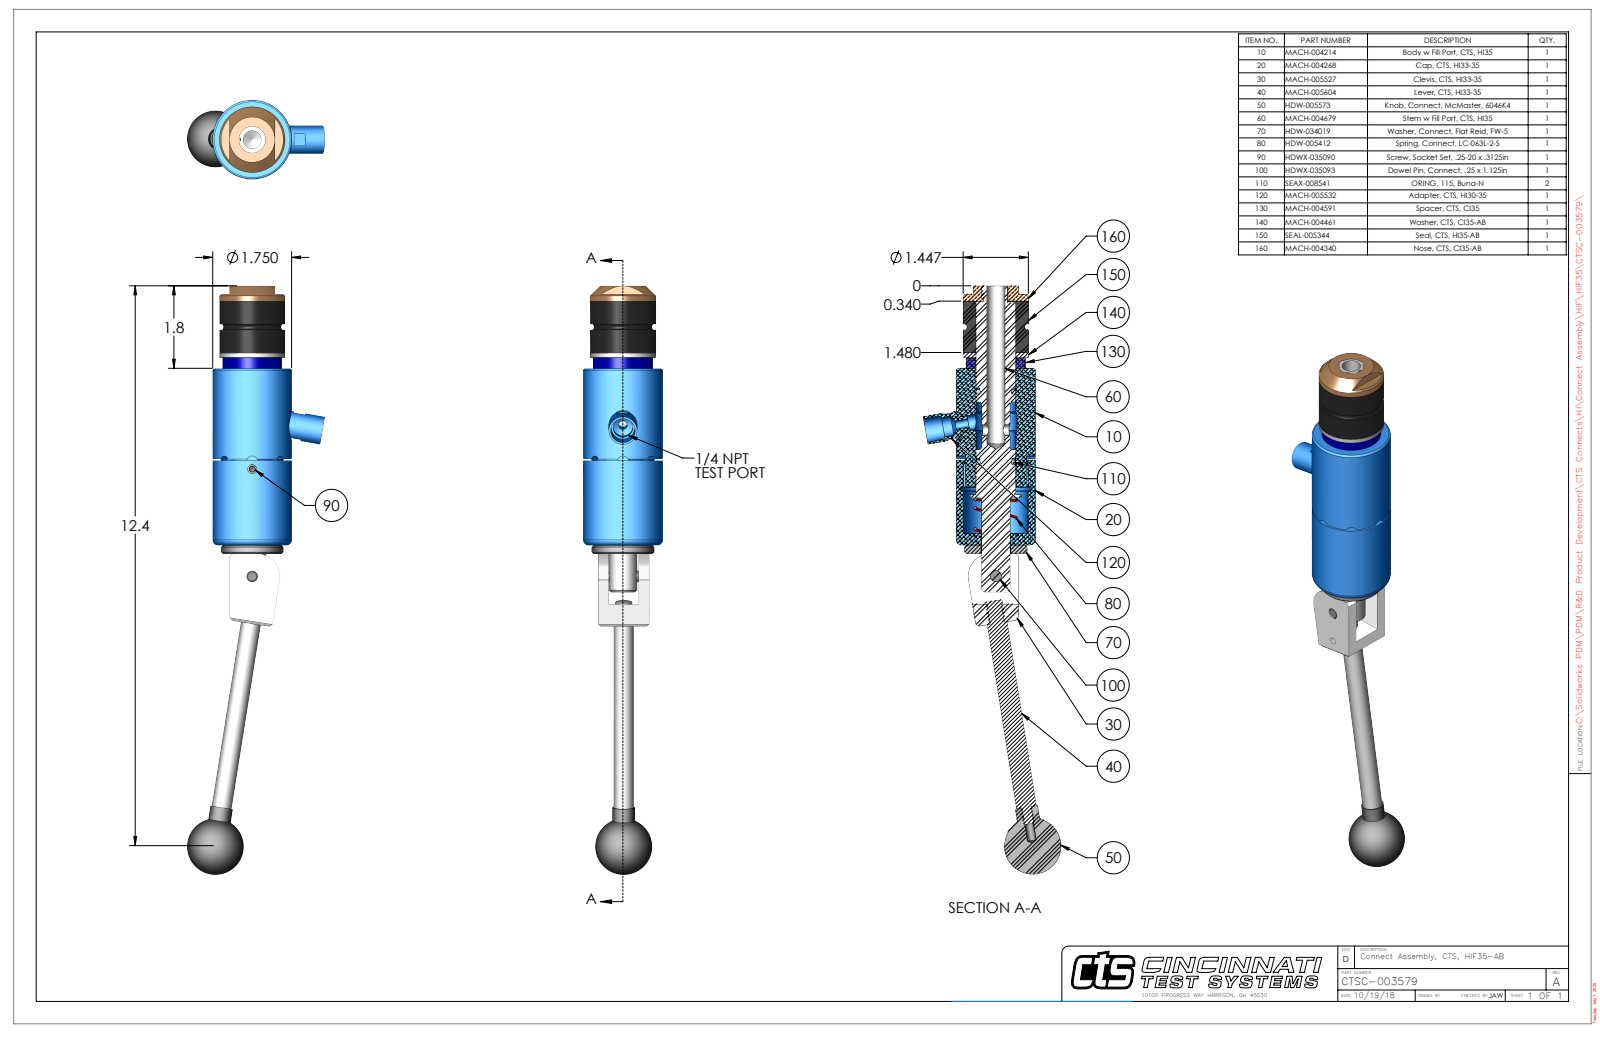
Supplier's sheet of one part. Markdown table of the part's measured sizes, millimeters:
| quantity | value |
| --- | --- |
| part name | CTSC-003579 |
| STEP written by | SolidWorks 2023 (AUTOMOTIVE_DESIGN) |
| units | millimeters |
| bodies | 11 solids, 298 faces (107 planar, 124 cylindrical, 67 other) |
| overall size | 331.3 × 77.3 × 44.5 |
| volume | 246 100 mm³ |
| surface area | 58 890 mm² |
| round holes (diameter × count) | 5.1 × 2, 3.8 × 1, 4.7 × 1, 6.3 × 1, 6.4 × 1, 6.4 × 1, 8 × 1, 10.3 × 1, 11.1 × 1, 13.5 × 1, 16.1 × 1, 16.7 × 1 |
| round bosses / shafts (diameter × count) | 6.4 × 2, 44.5 × 1, 36.8 × 1, 35.1 × 1, 33.3 × 1, 22.1 × 1, 15.9 × 1, 15.7 × 1 |
| partial cylindrical surfaces (radius × count) | 3.2 × 4, 0.7 × 2, 4.2 × 1, 4.2 × 1, 6.3 × 1, 8.4 × 1, 12.7 × 1, 17.7 × 1 |
| main face-to-face distances | 137.3, 37.8, 99.4, 29, 8.9, 108.3, 31.8, 2.8, 6.1, 105.5 |
| hole center spacings | 18.8, 60.4, 79.1 |
